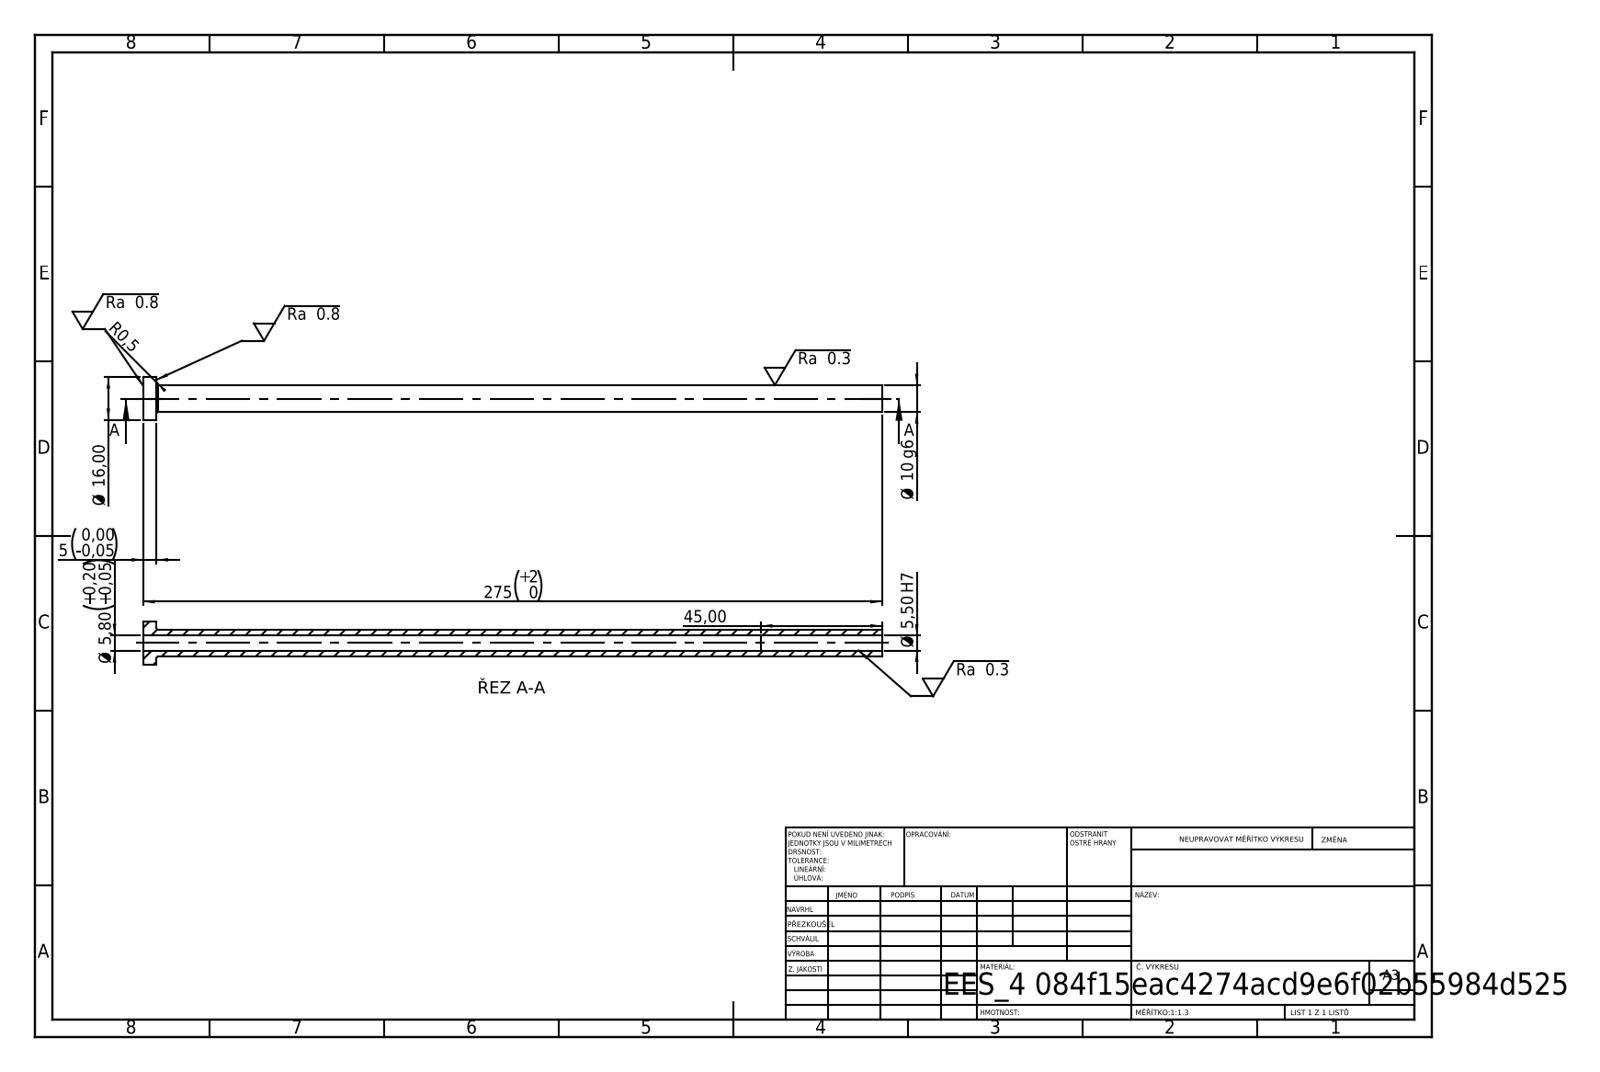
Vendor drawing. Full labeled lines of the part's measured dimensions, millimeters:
STEP written by: SolidWorks 2019 (CONFIG_CONTROL_DESIGN)
Units: millimetres
Bodies: 1 solid, 14 faces (4 planar, 8 cylindrical, 2 other)
Overall size (bounding box): 275 × 16 × 16
Volume: 15 067 mm³ · Surface area: 14 050 mm²
Round holes (diameter × count): ⌀5.5 ×1, ⌀5.8 ×1
Round bosses / shafts (diameter × count): ⌀16 ×1, ⌀10 ×1
Main face-to-face distances: 5, 275, 270, 230, 225, 45
